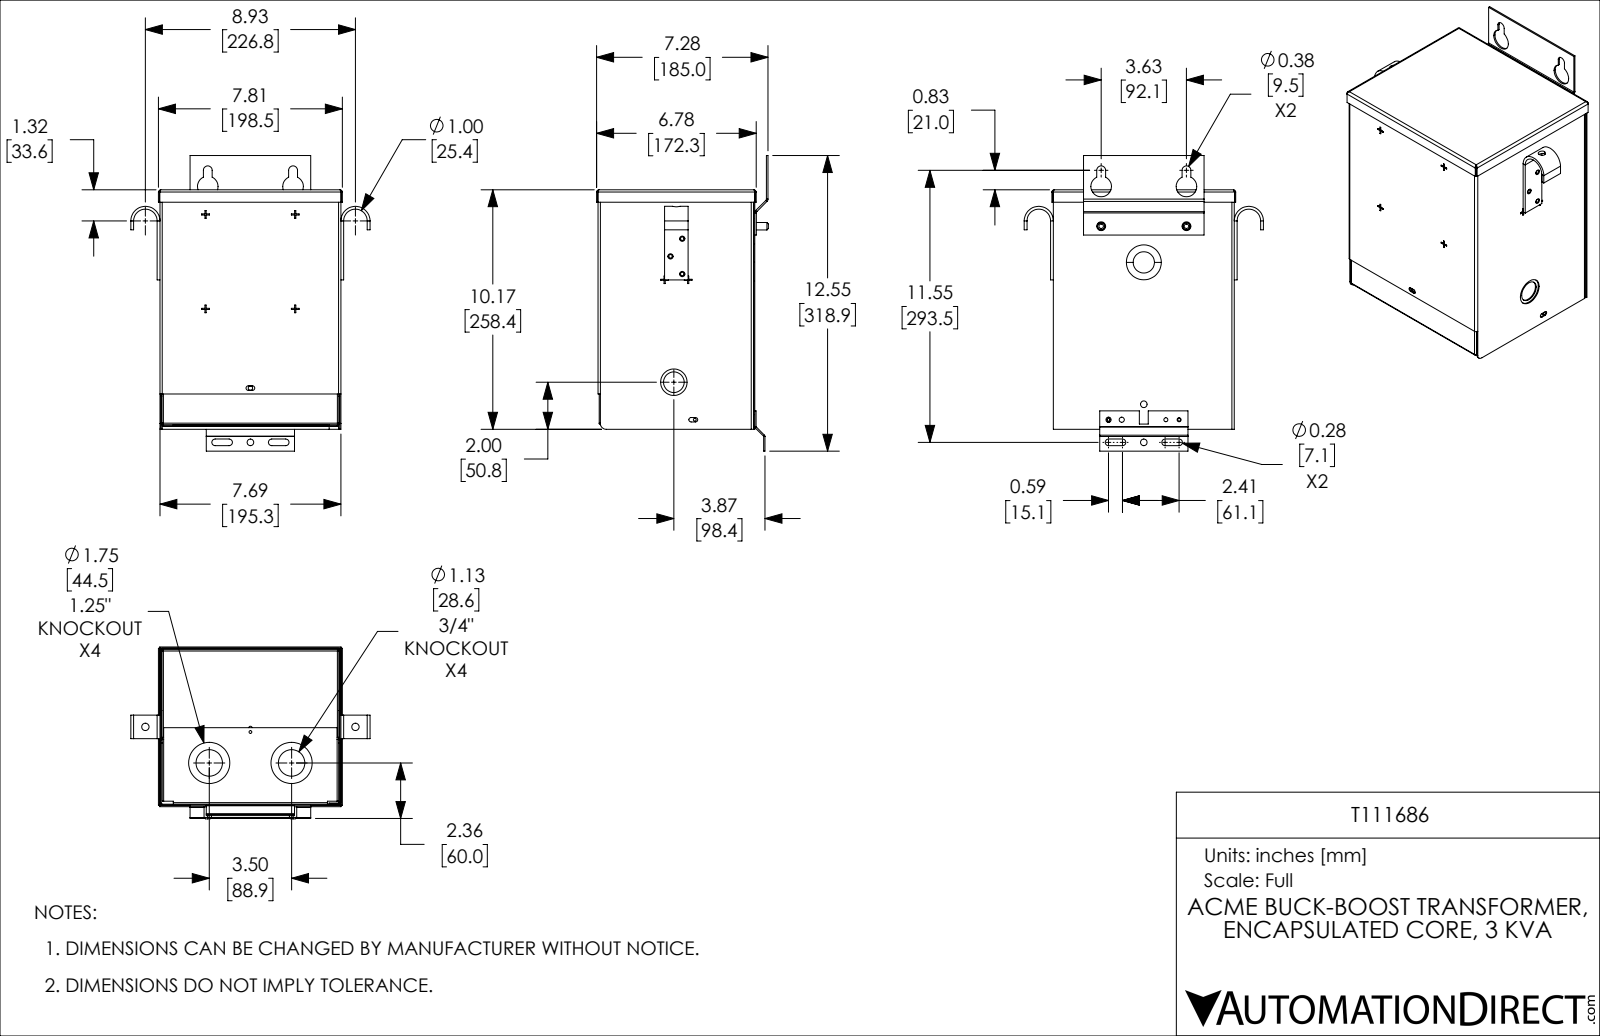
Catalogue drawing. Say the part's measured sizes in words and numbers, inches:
The part is named "T111686". Its 3-D file was written by "SolidWorks 2021 (CONFIG_CONTROL_DESIGN)". It is 10 solids with 634 faces: 424 planar, 150 cylindrical and 60 other. Overall it measures 12.554 by 10.167 by 7.298 inches. Its volume is 22.01 cubic inches and its surface area 927.7 square inches. Round holes: 4 of diameter 0.12, 4 of diameter 0.313, 3 of diameter 0.875, 3 of diameter 1.125, 2 of diameter 0.172, 2 of diameter 0.187, 2 of diameter 0.219, 2 of diameter 0.281, 2 of diameter 0.375, 2 of diameter 1.75, 1 of diameter 0.173. Round bosses or shafts: 3 of diameter 1.173, 2 of diameter 1.798, 2 of diameter 0.312, 1 of diameter 0.923. Partial cylindrical surfaces (rounded edges, fillets, slot ends): 11 of radius 0.05, 8 of radius 0.094, 8 of radius 0.098, 5 of radius 0.015, 5 of radius 0.063, 4 of radius 0.141, 3 of radius 0.065, 2 of radius 0.02. The main face-to-face distances are 0.048, 6.612, 7.64, 6.565, 7.687, 6.66, 7.592, 9.929, 0.015, 0.048. The hole center spacings are 0.563, 1.145, 1.342, 1.638, 1.638, 1.687, 1.781, 2.014.
